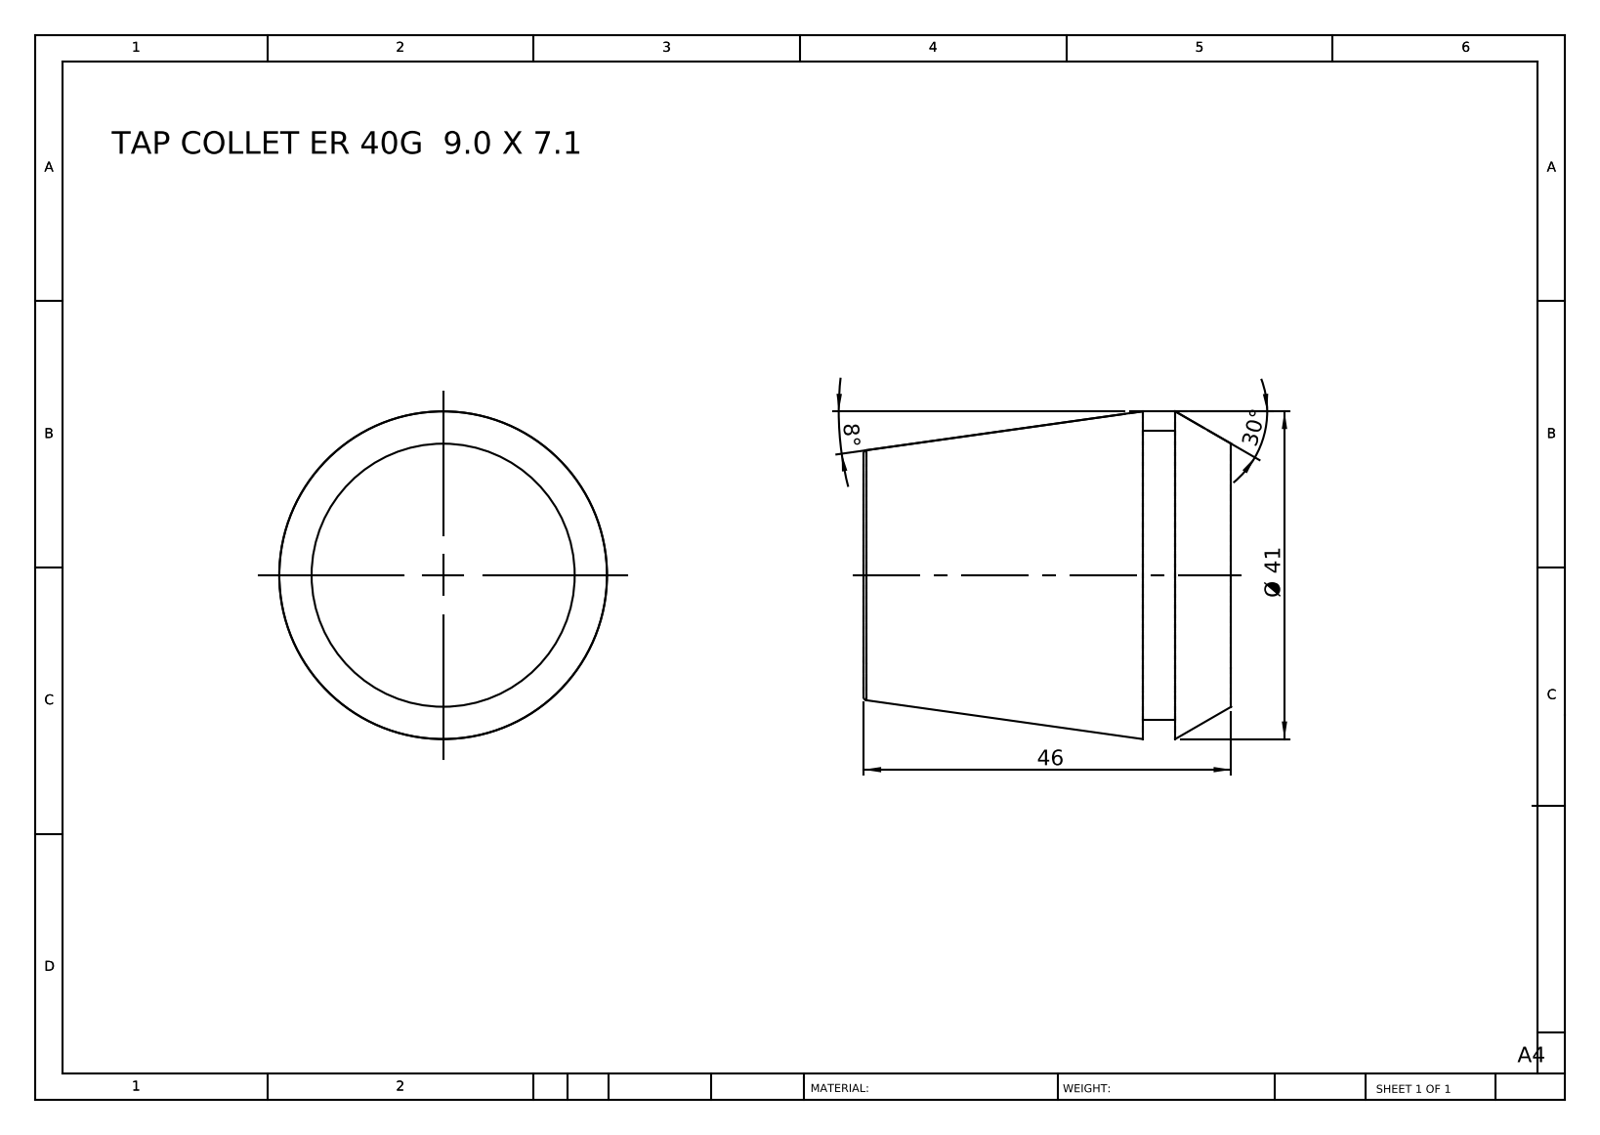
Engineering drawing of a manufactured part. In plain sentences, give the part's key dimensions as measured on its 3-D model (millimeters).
The part is named "TAP COLLET ER 40G 9.0 X 7.1". Its 3-D file was written by "SolidWorks 2014 (CONFIG_CONTROL_DESIGN)". It is 1 solid with 12 faces: 4 planar, 2 cylindrical and 6 other. Overall it measures 46 by 41 by 41 millimeters. Its volume is 47 690 cubic millimeters and its surface area 7 586 square millimeters. Round bosses or shafts: 1 of diameter 36.2. The main face-to-face distances are 46, 11.1, 34.9, 7, 4.1, 39.
